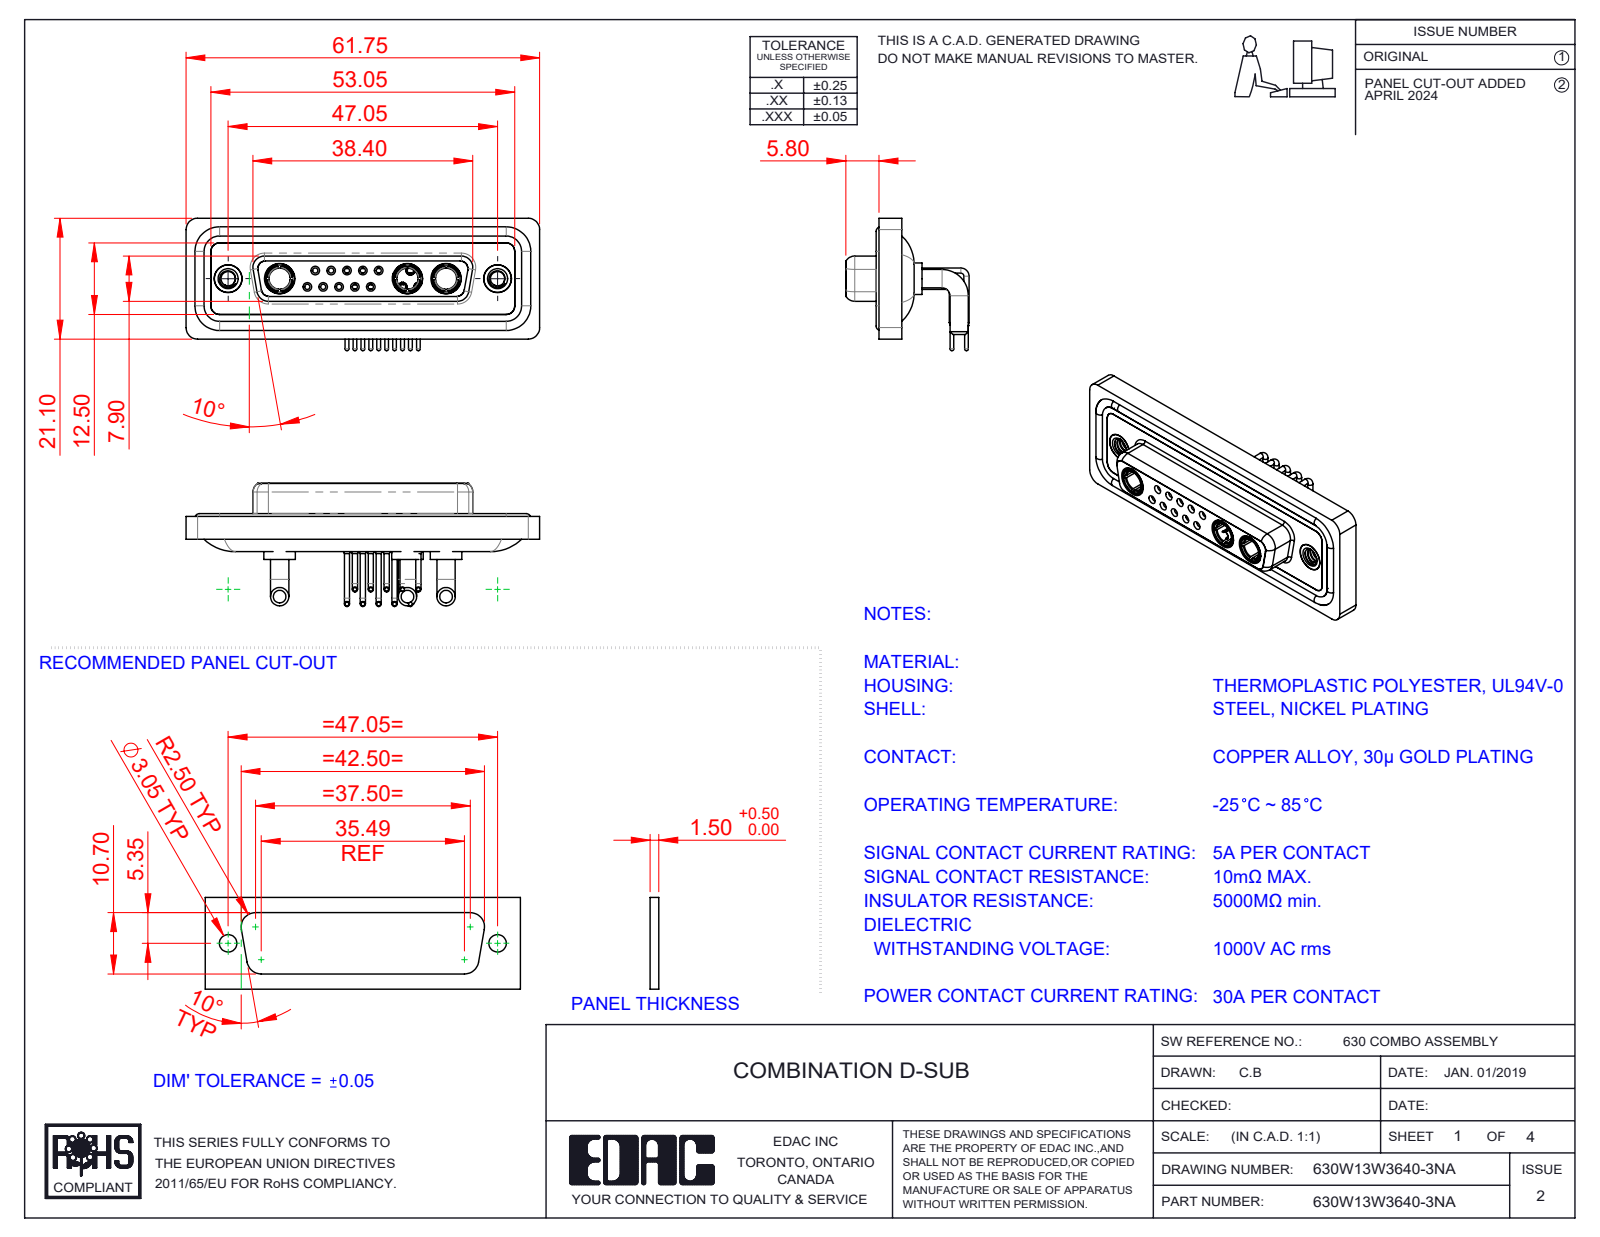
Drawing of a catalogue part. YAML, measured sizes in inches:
part_name: "Power Socket_30A RA; 630Combo Housing_13W3; 630Combo Shell Rear_25 Contacts; 630Combo Threaded Rivet_A (+5 more)"
step_written_by: "SolidWorks 2023 (CONFIG_CONTROL_DESIGN)"
units: inches
bodies: {solids: 23, faces: 1144, planar: 342, cylindrical: 491, other: 311}
overall_size: [2.431, 0.91, 0.848]
volume: 0.522
surface_area: 22.25
round_holes:
  - {diameter: 0.035, count: 10}
  - {diameter: 0.043, count: 10}
  - {diameter: 0.059, count: 10}
  - {diameter: 0.079, count: 10}
  - {diameter: 0.063, count: 5}
  - {diameter: 0.067, count: 5}
  - {diameter: 0.191, count: 5}
  - {diameter: 0.146, count: 3}
  - {diameter: 0.209, count: 3}
  - {diameter: 0.098, count: 2}
  - {diameter: 0.157, count: 2}
  - {diameter: 0.159, count: 2}
round_bosses_or_shafts:
  - {diameter: 0.035, count: 15}
  - {diameter: 0.063, count: 12}
  - {diameter: 0.026, count: 10}
  - {diameter: 0.126, count: 6}
  - {diameter: 0.079, count: 5}
  - {diameter: 0.059, count: 5}
  - {diameter: 0.217, count: 3}
  - {diameter: 0.205, count: 3}
partial_cylinders:
  - {radius: 0.059, count: 18}
  - {radius: 0.079, count: 18}
  - {radius: 0.053, count: 8}
  - {radius: 0.063, count: 8}
  - {radius: 0.01, count: 4}
  - {radius: 0.02, count: 4}
  - {radius: 0.024, count: 4}
  - {radius: 0.026, count: 4}
face_to_face_distances: [0.016, 0.071, 0.161, 0.043, 0.063, 0.122, 0.059, 0.098, 0.146, 0.055]
hole_center_spacings: [0.124, 0.109, 0.218, 0.198, 0.327, 0.198, 0.295, 0.436]
